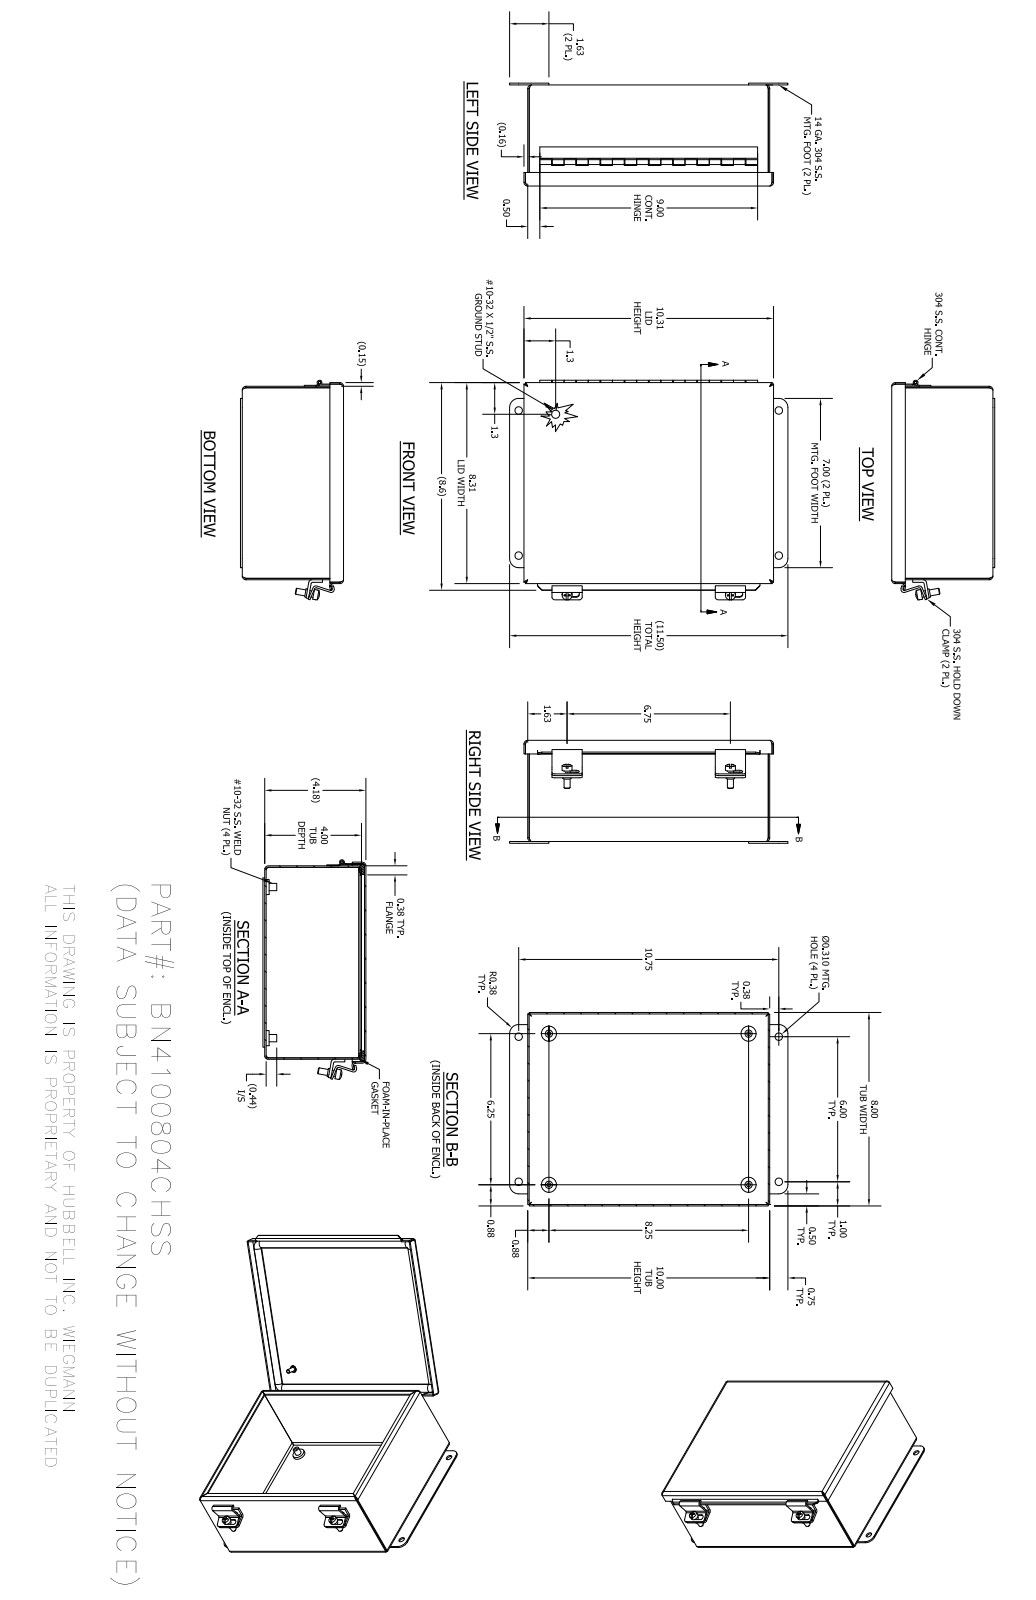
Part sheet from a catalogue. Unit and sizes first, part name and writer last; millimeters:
Units: millimetres
Overall size (bounding box): 292.1 × 230.78 × 108.11
Round holes (diameter × count): ⌀2.79 ×4, ⌀3.96 ×4, ⌀7.87 ×4, ⌀4.98 ×2, ⌀2.96 ×1
Round bosses / shafts (diameter × count): ⌀15.88 ×4, ⌀7.62 ×4, ⌀10.4 ×2, ⌀8.74 ×2, ⌀6.35 ×2, ⌀8.56 ×1, ⌀5.08 ×1, ⌀4.83 ×1
Partial cylindrical surfaces — rounded edges, fillets, slot ends (radius × count): R2.38 ×13, R3.88 ×13, R1.68 ×8, R3.17 ×8, R3.38 ×4, R5.78 ×4, R9.53 ×4, R1.6 ×3
Main face-to-face distances: 1.5, 104.71, 106.21, 103.21, 201.7, 252.5, 203.2, 200.2, 254, 251
Hole centre spacings: 31.91, 152.4, 171.45, 241.32, 19.05, 158.75, 158.79, 209.55
Volume: 423 140 mm³ · Surface area: 526 382 mm²
Bodies: 19 solids, 448 faces (244 planar, 137 cylindrical, 67 other)
Part name (STEP PRODUCT): B_100804_SSBKP; H4050549LH; H4050549P; H4050549TH (+8 more)
STEP written by: Autodesk Inventor 2016 (AUTOMOTIVE_DESIGN)
